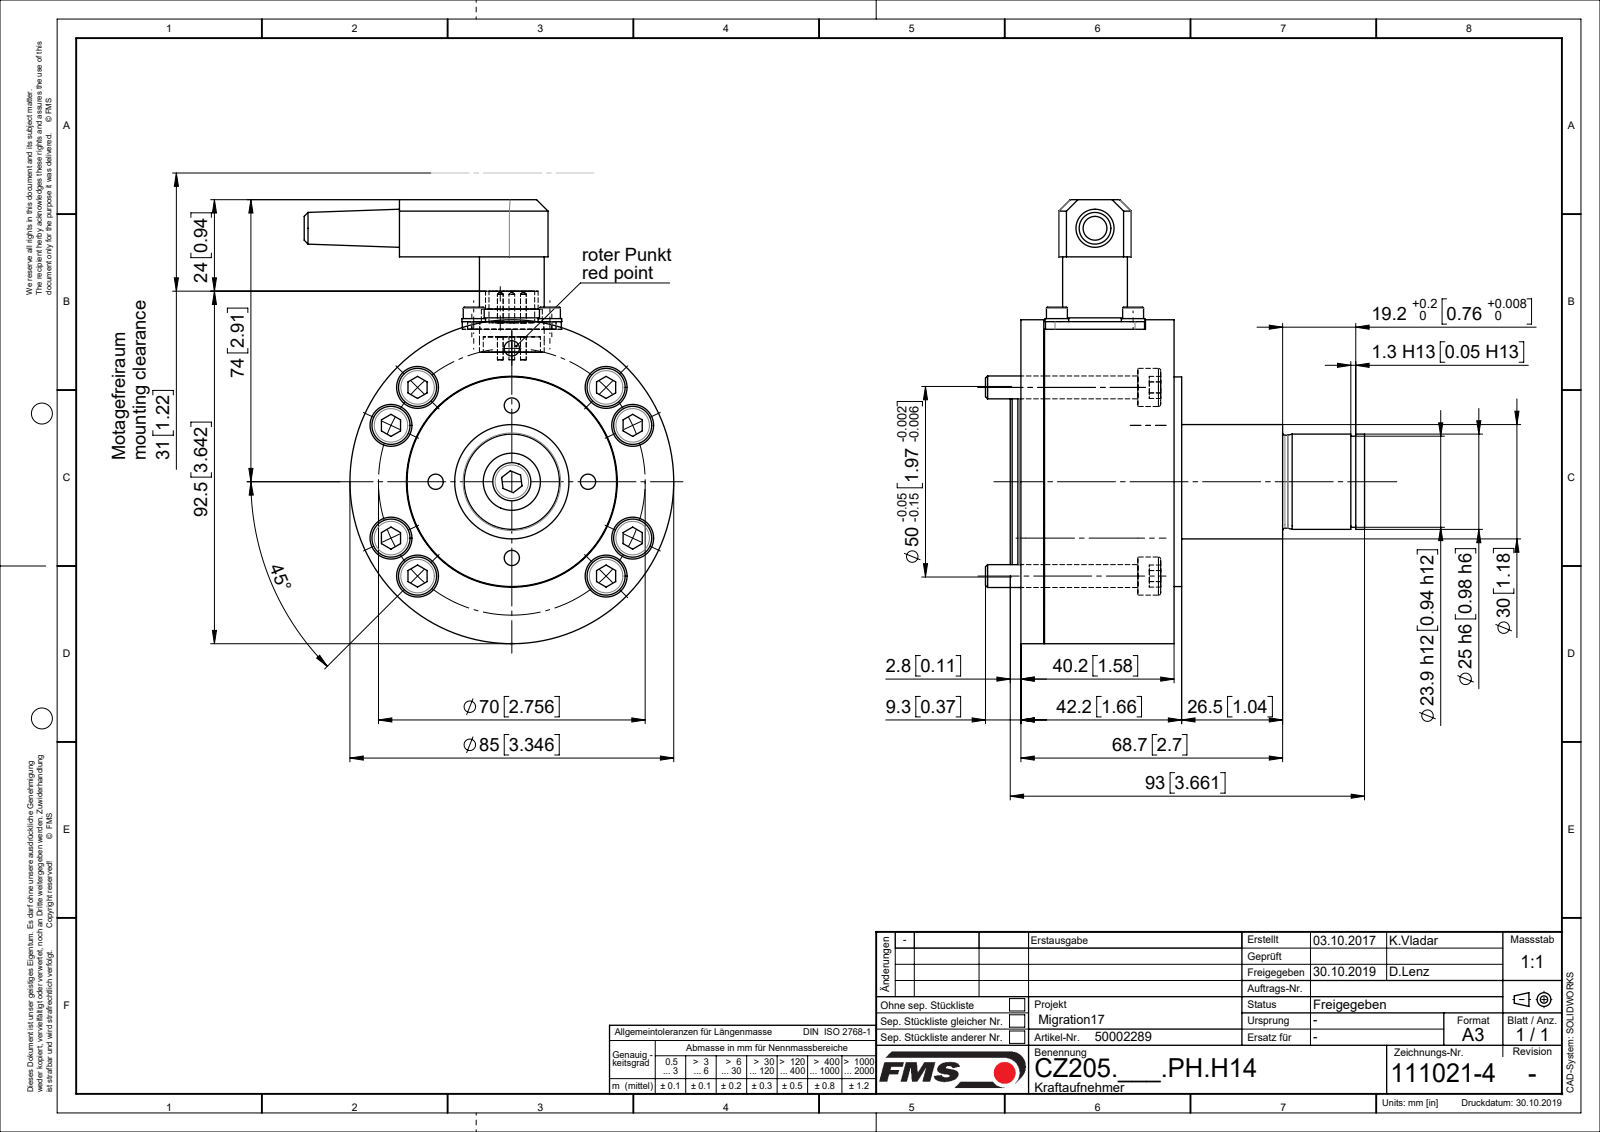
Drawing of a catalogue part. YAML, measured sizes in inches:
part_name: "ZEICHNUNG7; C1110214; C0709081; C0612056 (+8 more)"
step_written_by: "Mechanical Desktop 2009 (CONFIG_CONTROL_DESIGN)"
units: inches
bodies: {solids: 27, faces: 552, planar: 197, cylindrical: 256, other: 99}
overall_size: [4.587, 3.917, 3.819]
volume: 13.85
surface_area: 130.5
round_holes:
  - {diameter: 0.256, count: 8}
  - {diameter: 0.433, count: 8}
  - {diameter: 0.079, count: 5}
  - {diameter: 0.102, count: 4}
  - {diameter: 0.126, count: 4}
  - {diameter: 0.157, count: 4}
  - {diameter: 0.203, count: 4}
  - {diameter: 0.276, count: 4}
  - {diameter: 0.591, count: 2}
  - {diameter: 0.281, count: 1}
  - {diameter: 0.354, count: 1}
  - {diameter: 0.42, count: 1}
round_bosses_or_shafts:
  - {diameter: 0.394, count: 8}
  - {diameter: 0.236, count: 8}
  - {diameter: 0.059, count: 5}
  - {diameter: 0.244, count: 4}
  - {diameter: 0.217, count: 4}
  - {diameter: 0.197, count: 4}
  - {diameter: 0.118, count: 4}
  - {diameter: 3.346, count: 1}
partial_cylinders:
  - {radius: 0.098, count: 4}
  - {radius: 0.197, count: 2}
  - {radius: 0.374, count: 1}
face_to_face_distances: [0.236, 0.079, 0.118, 1.339, 1.575, 1.654, 1.417, 1.319, 1.772, 1.26]
hole_center_spacings: [0.787, 0.992, 1.378, 2.013, 1.113, 0.479, 0.557, 0.743]
